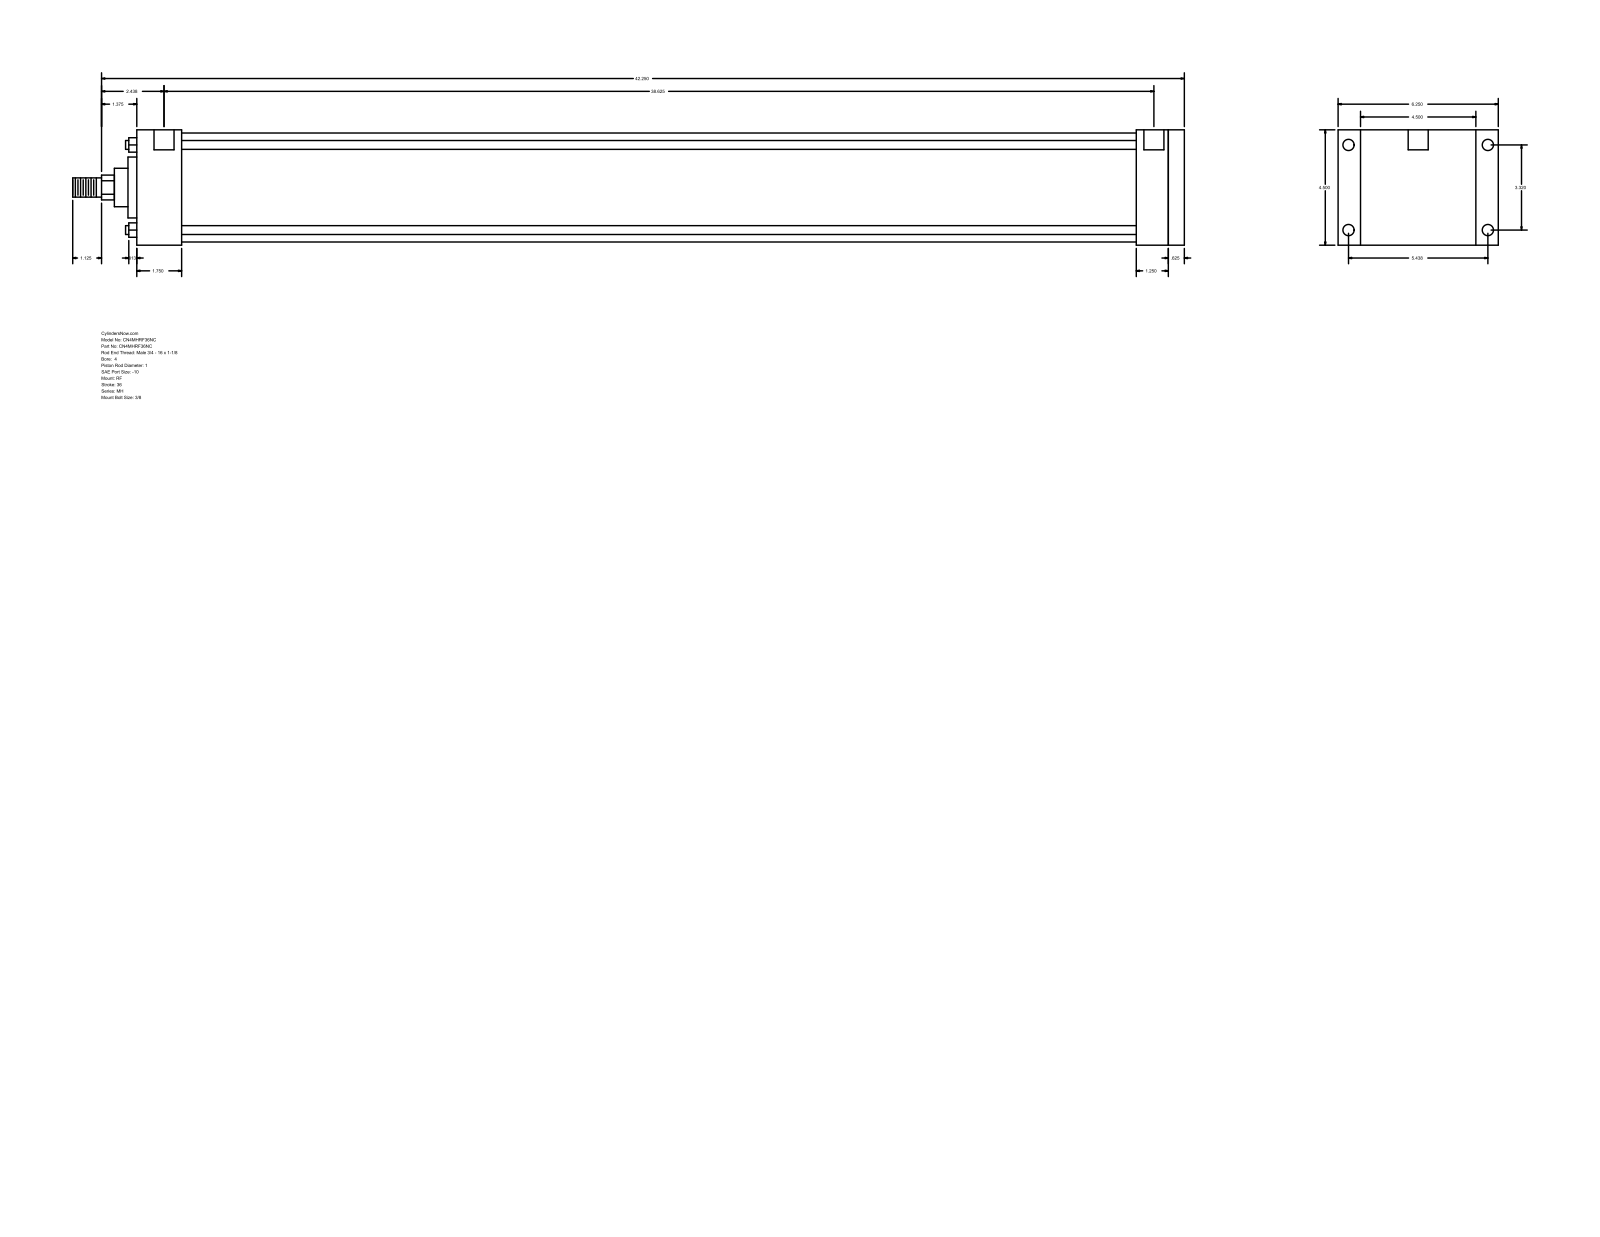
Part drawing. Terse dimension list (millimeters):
name: MH_RF__0400_1
written by: GSSL Pune (CONFIG_CONTROL_DESIGN)
unit: mm
bodies: 0 solids, 94 faces (65 planar, 29 cylindrical, 0 other)
size: 1101.72 × 158.75 × 114.3
holes: 4× ⌀8.73, 4× ⌀11.13, 2× ⌀19.84
bosses: 4× ⌀8.76, 1× ⌀107.95, 1× ⌀60.33, 1× ⌀38.1, 1× ⌀25.4, 1× ⌀19.05
rounds: 1× R12.29
face distances: 114.3, 1038.23, 1022.36, 15.87, 44.46, 977.9, 993.77, 990.61, 946.15, 31.75
hole spacings: 84.32, 138.12, 161.82, 984.25, 1.58, 1.59, 981.08, 982.66
